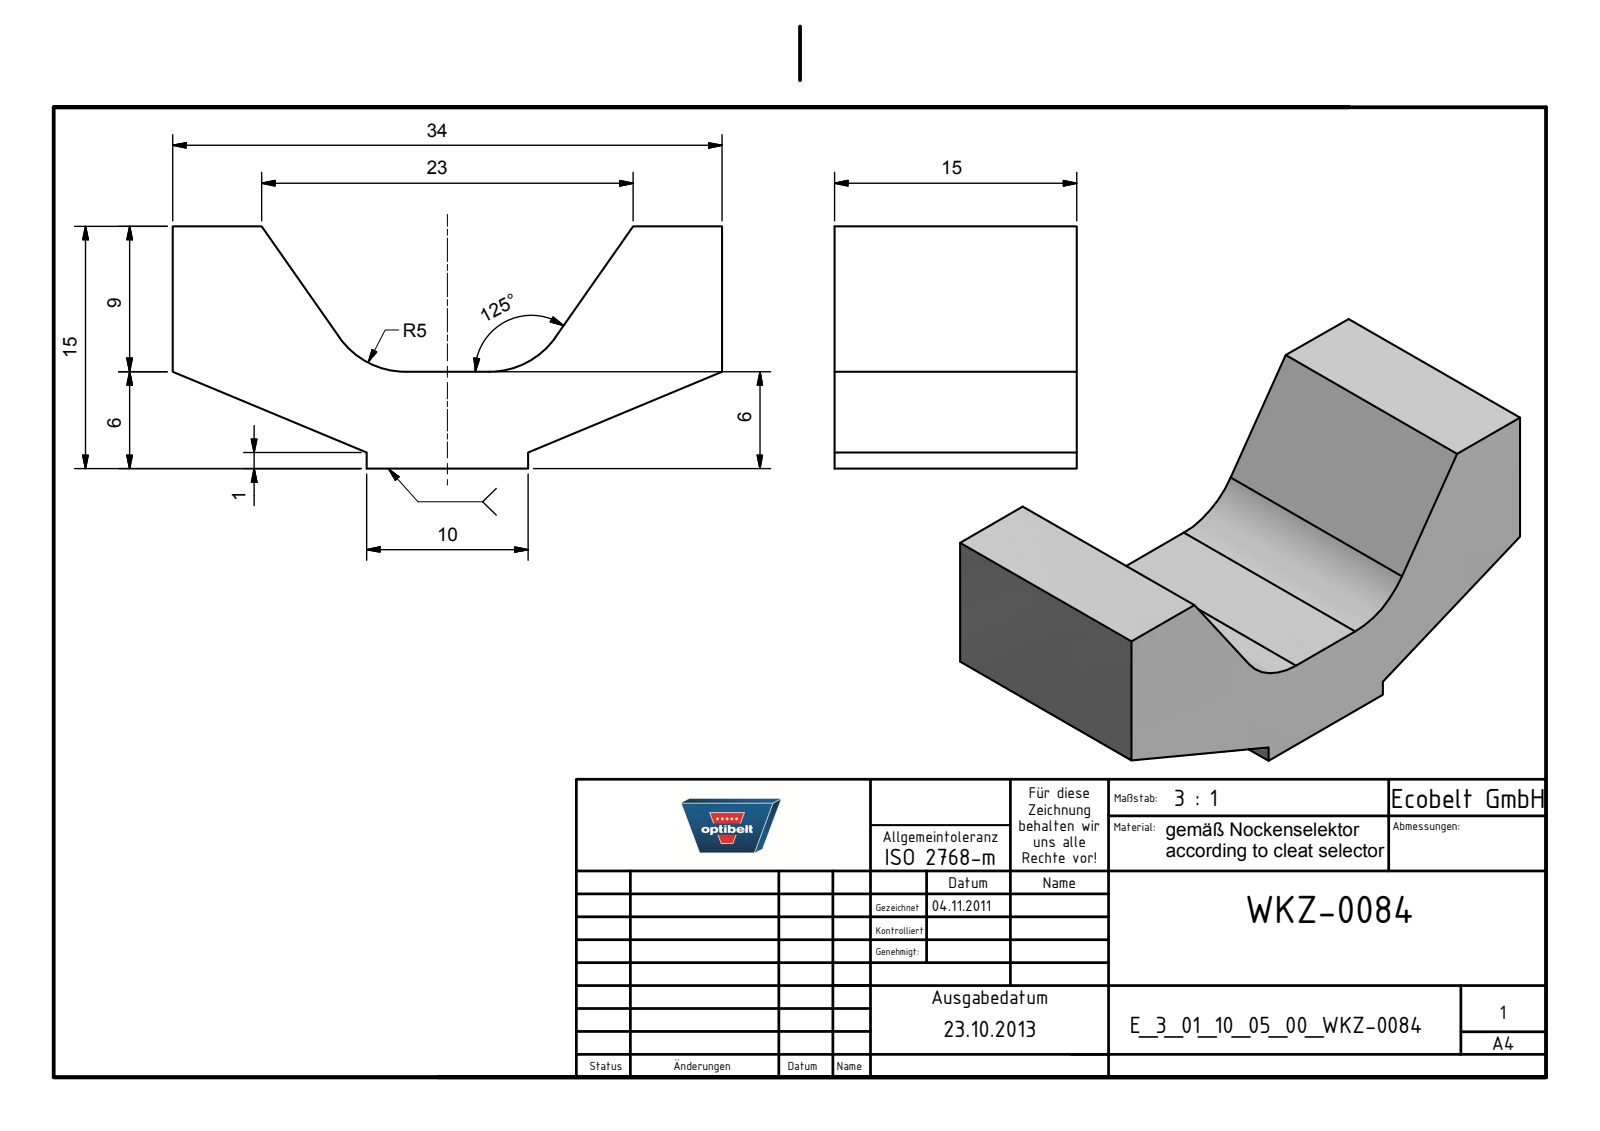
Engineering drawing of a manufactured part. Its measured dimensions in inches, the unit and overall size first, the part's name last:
Units: inches
Overall size (bounding box): 1.339 × 0.591 × 0.591
Partial cylindrical surfaces — rounded edges, fillets, slot ends (radius × count): R0.197 ×2
Main face-to-face distances: 0.591, 1.339, 0.236, 0.354, 0.472, 0.866, 0.394
Volume: 0.254 in³ · Surface area: 3.153 in²
Bodies: 1 solid, 16 faces (14 planar, 2 cylindrical, 0 other)
Part name (STEP PRODUCT): E_3_01_10_05_00_WKZ-0084
STEP written by: Autodesk Inventor 2025 (AUTOMOTIVE_DESIGN)
